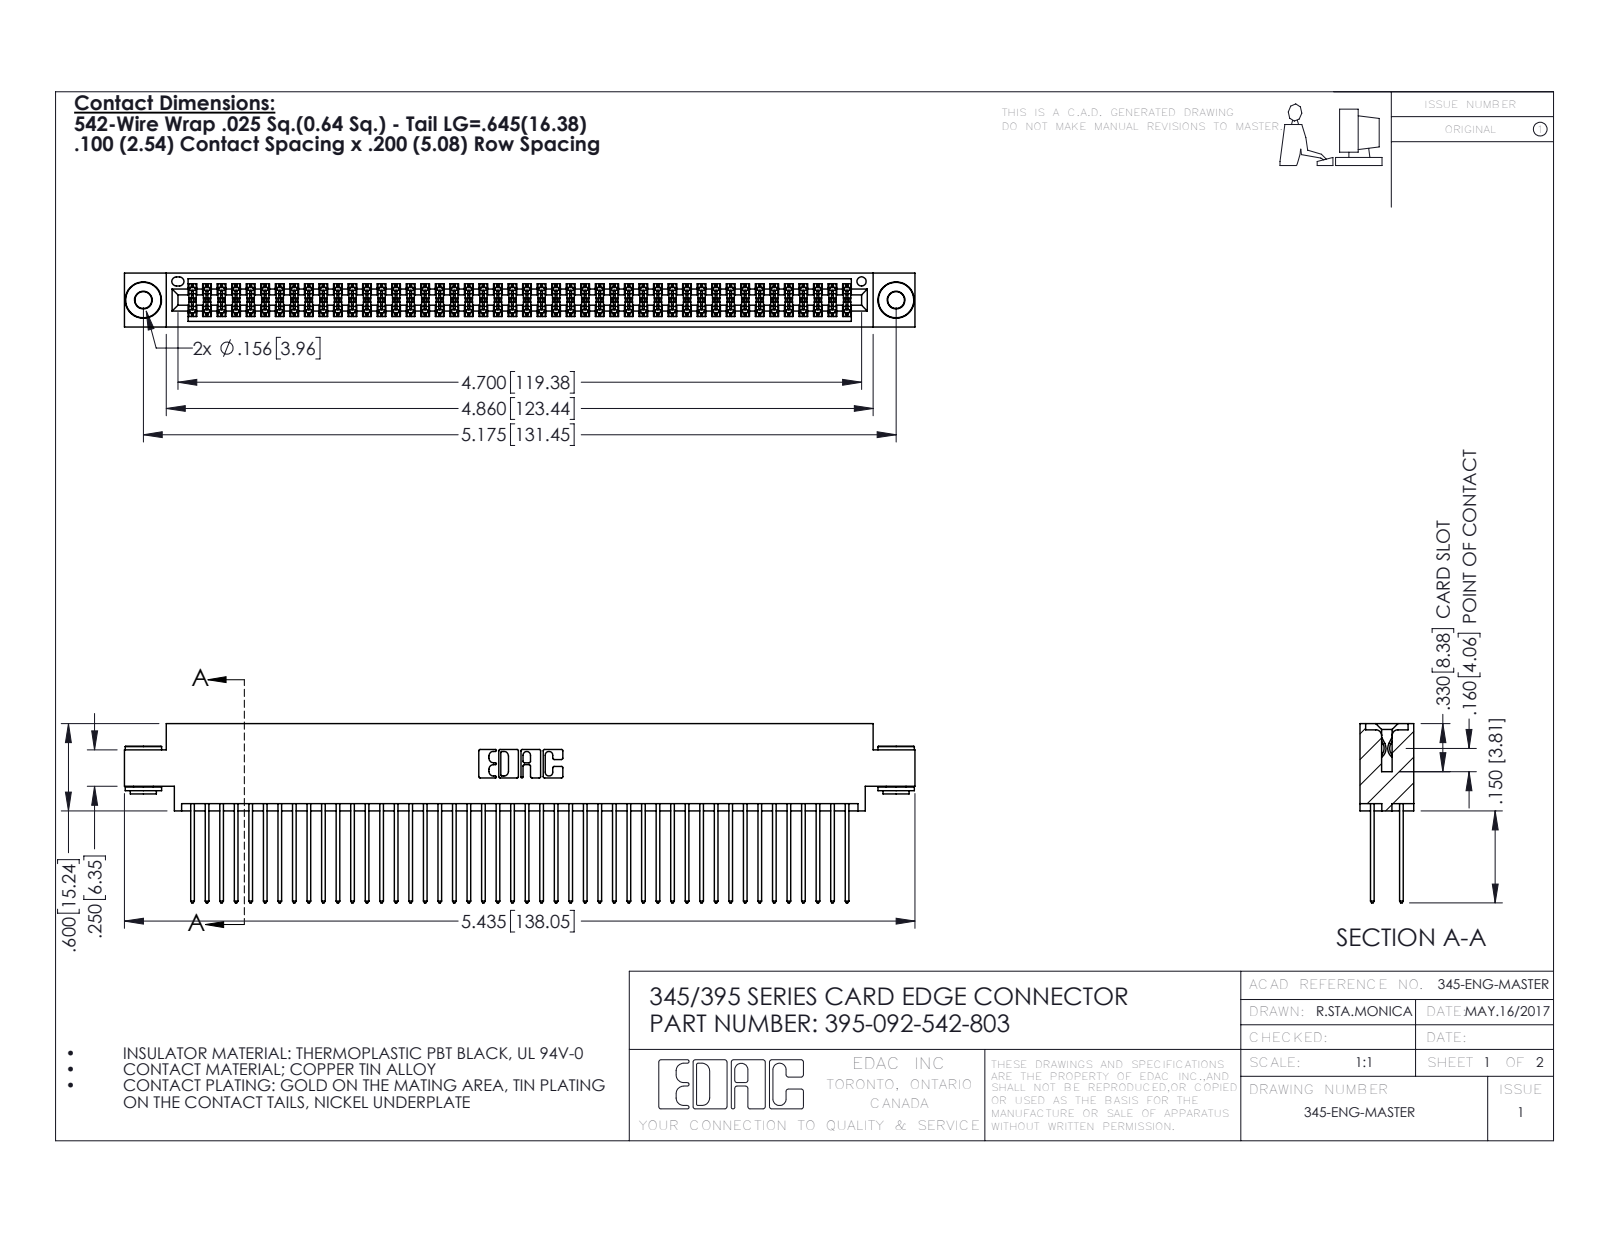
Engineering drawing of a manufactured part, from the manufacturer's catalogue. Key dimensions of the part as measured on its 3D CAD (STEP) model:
Part name (STEP PRODUCT): 345 Part_0.170 Offset - 0.156 Dia-TH; 395-092-542-803; 345-250-002_345-250-002-102; 345-292-001_345-293-142
STEP written by: SolidWorks 2016 (CONFIG_CONTROL_DESIGN)
Units: inches
Bodies: 95 solids, 4768 faces (3130 planar, 1630 cylindrical, 8 other)
Overall size (bounding box): 5.435 × 1.232 × 0.37
Volume: 0.841 in³ · Surface area: 35.34 in²
Round holes (diameter × count): ⌀0.116 ×2, ⌀0.156 ×2, ⌀0.064 ×1
Round bosses / shafts (diameter × count): ⌀0.25 ×2, ⌀0.18 ×2, ⌀0.136 ×2
Partial cylindrical surfaces — rounded edges, fillets, slot ends (radius × count): R0.006 ×138, R0.01 ×92, R0.01 ×22, R0.007 ×6, R0.031 ×6, R0.026 ×3, R0.014 ×2, R0.019 ×2
Main face-to-face distances: 0.072, 0.298, 0.2, 0.098, 0.272, 0.025, 0.37, 0.225, 0.175, 0.149
Hole centre spacings: 0.27, 4.939, 5.175
